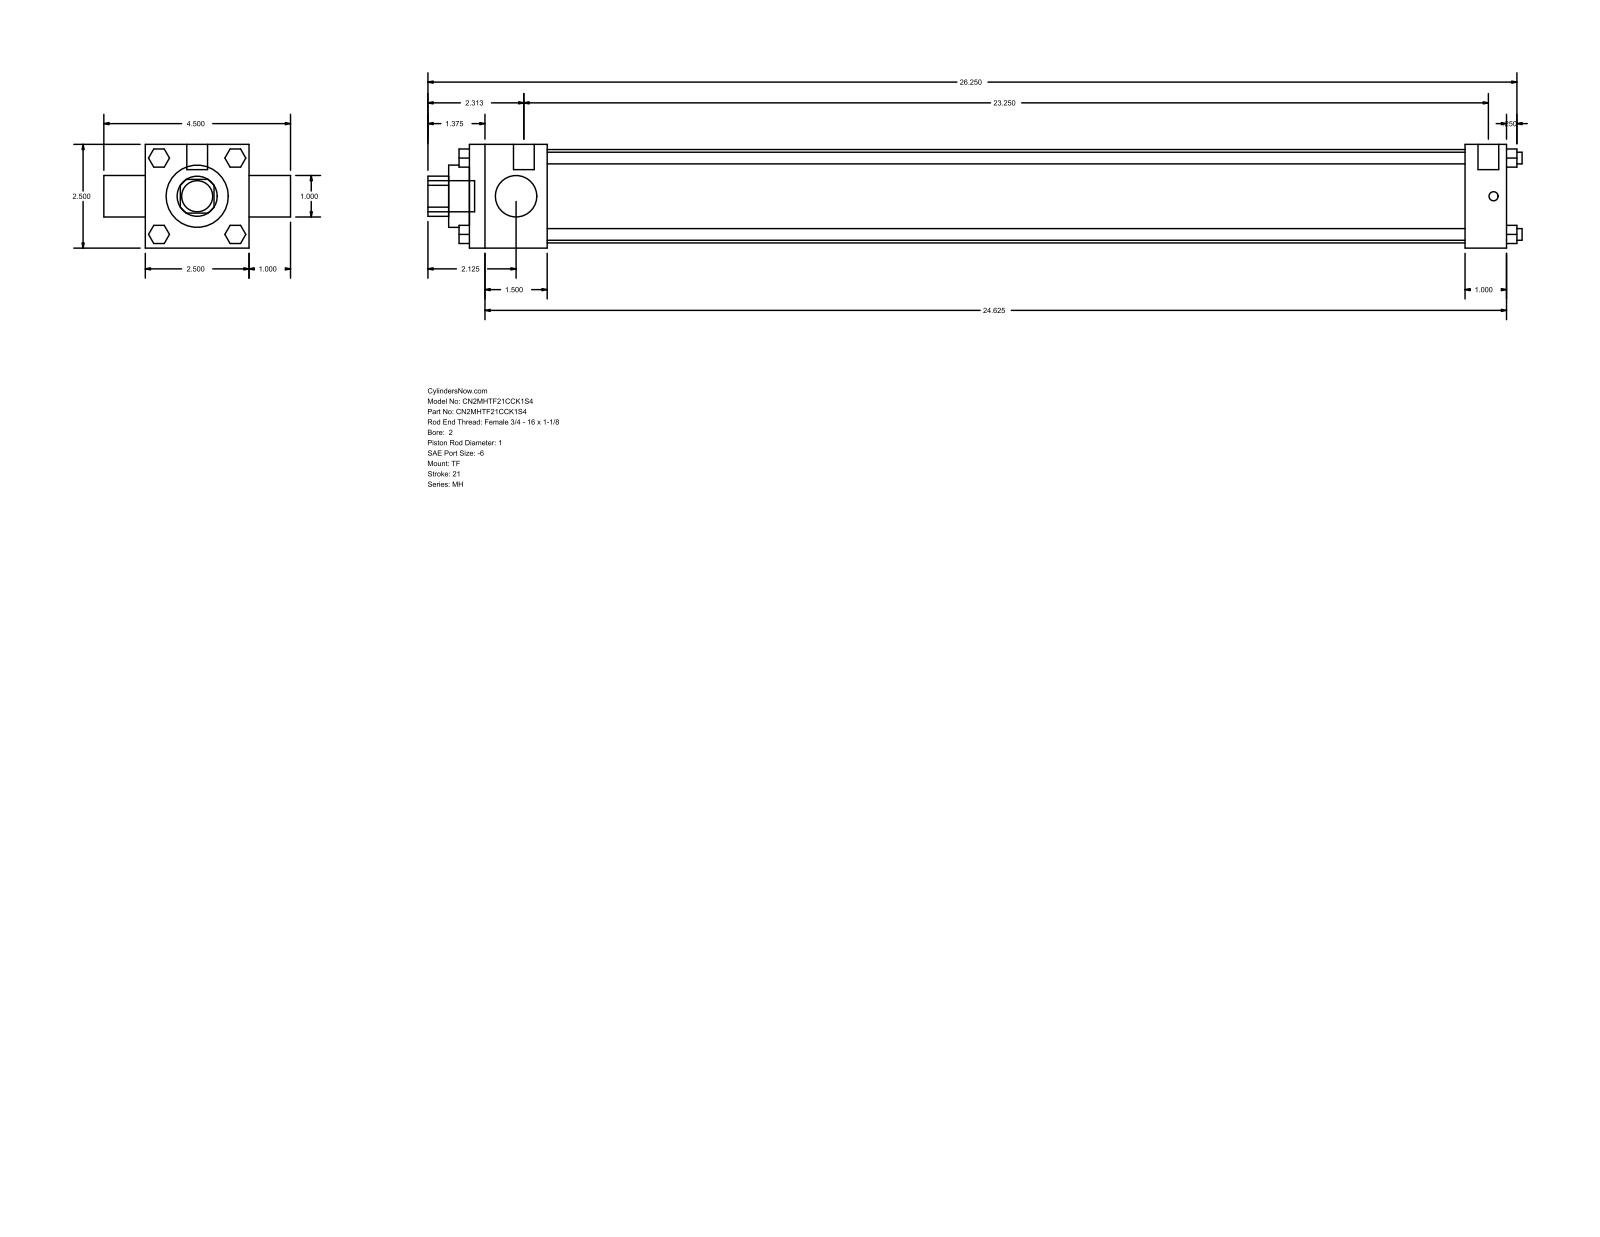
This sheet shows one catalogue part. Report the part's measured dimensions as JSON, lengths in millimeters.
{"part_name": "MH_TF__0200_1", "step_written_by": "GSSL Pune (CONFIG_CONTROL_DESIGN)", "units": "millimeters", "bodies": {"solids": 0, "faces": 120, "planar": 92, "cylindrical": 28, "other": 0}, "overall_size": [669.92, 114.3, 63.5], "round_holes": [[25.4, 2], [38.1, 1], [57.15, 1]], "round_bosses_or_shafts": [[7.14, 4], [5.56, 3], [12.7, 2], [19.05, 1]], "partial_cylinders_radius": [[12.29, 1]], "face_to_face_distances": [63.5, 635, 25.4, 47.63, 609.6, 561.97, 587.37, 88.9, 647.7, 6.35]}
